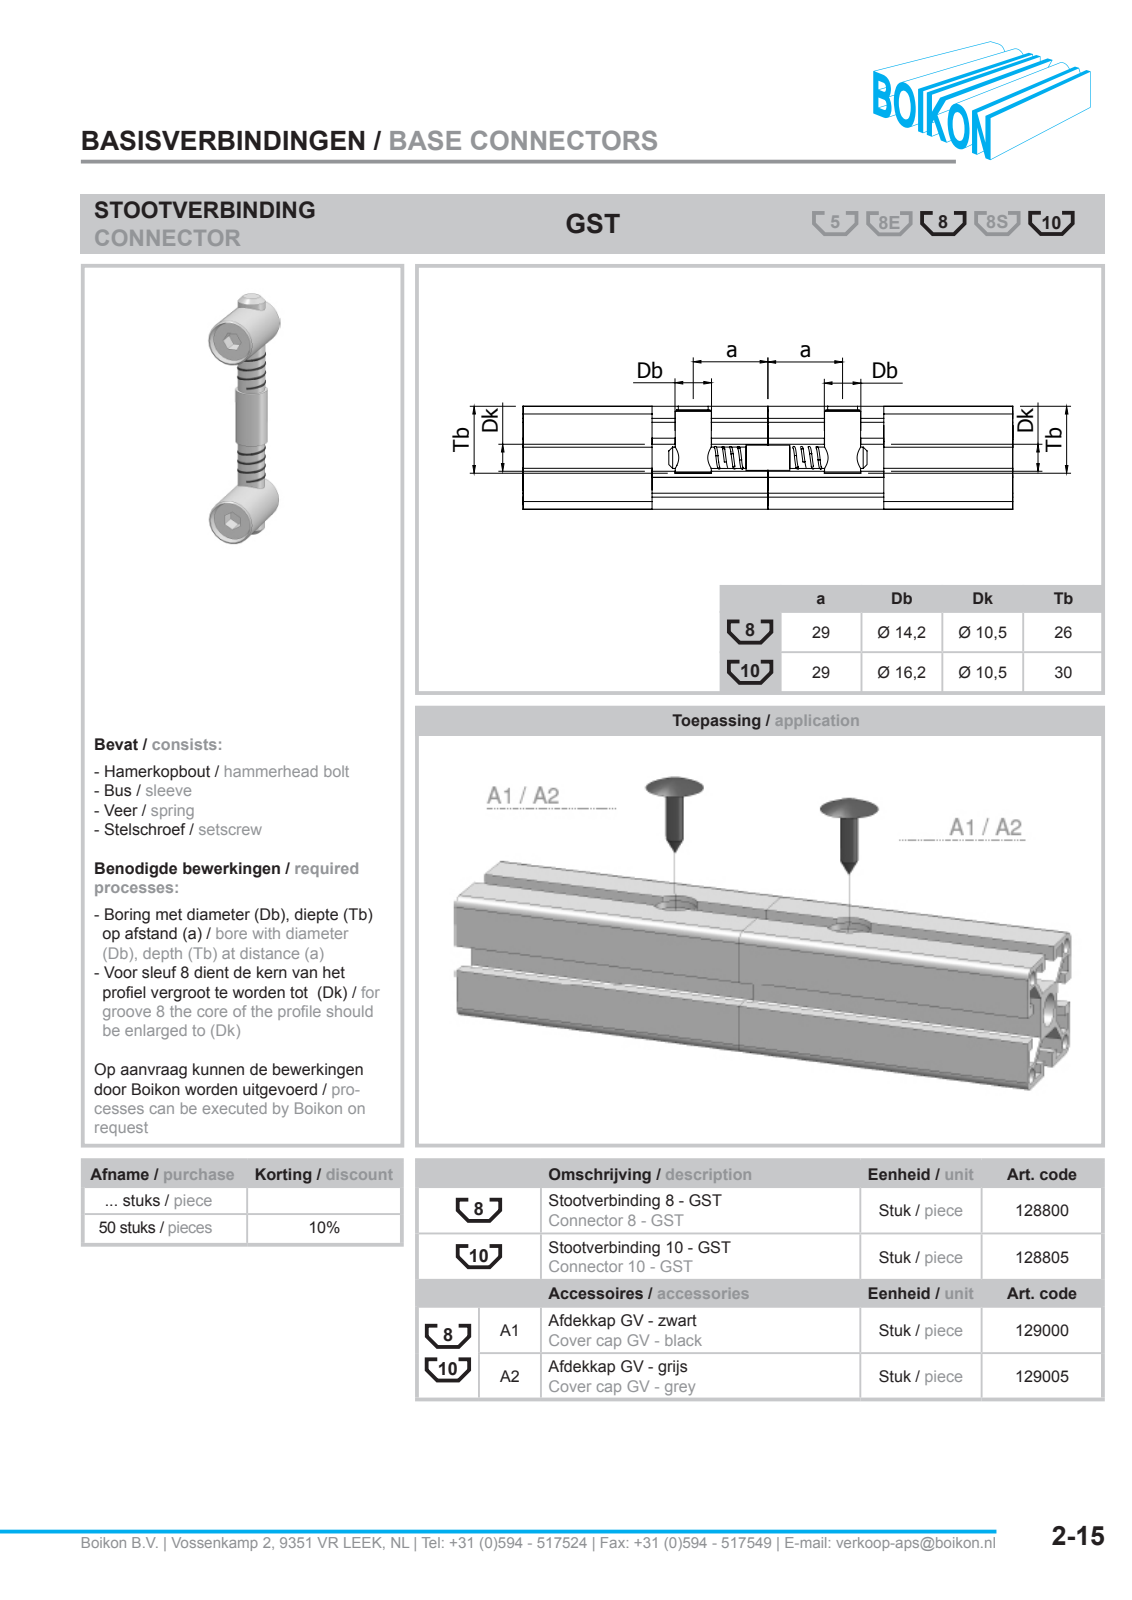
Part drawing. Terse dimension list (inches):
name: Root; 128805Stootverbinding 10 - GSTBOIKON
written by: HiCAD 2013 1802.4 Build 509 (AUTOMOTIVE_DESIGN)
unit: in
bodies: 1 solid, 33 faces (22 planar, 9 cylindrical, 2 other)
size: 3.031 × 1.142 × 0.63
volume: 0.845 in³; area: 8.251 in²
bosses: 2× ⌀0.63, 1× ⌀0.386, 1× ⌀0.327
face distances: 1.142, 0.236, 0.748, 0.394, 1.181, 1.85, 2.776, 2.539, 0.256, 0.492
